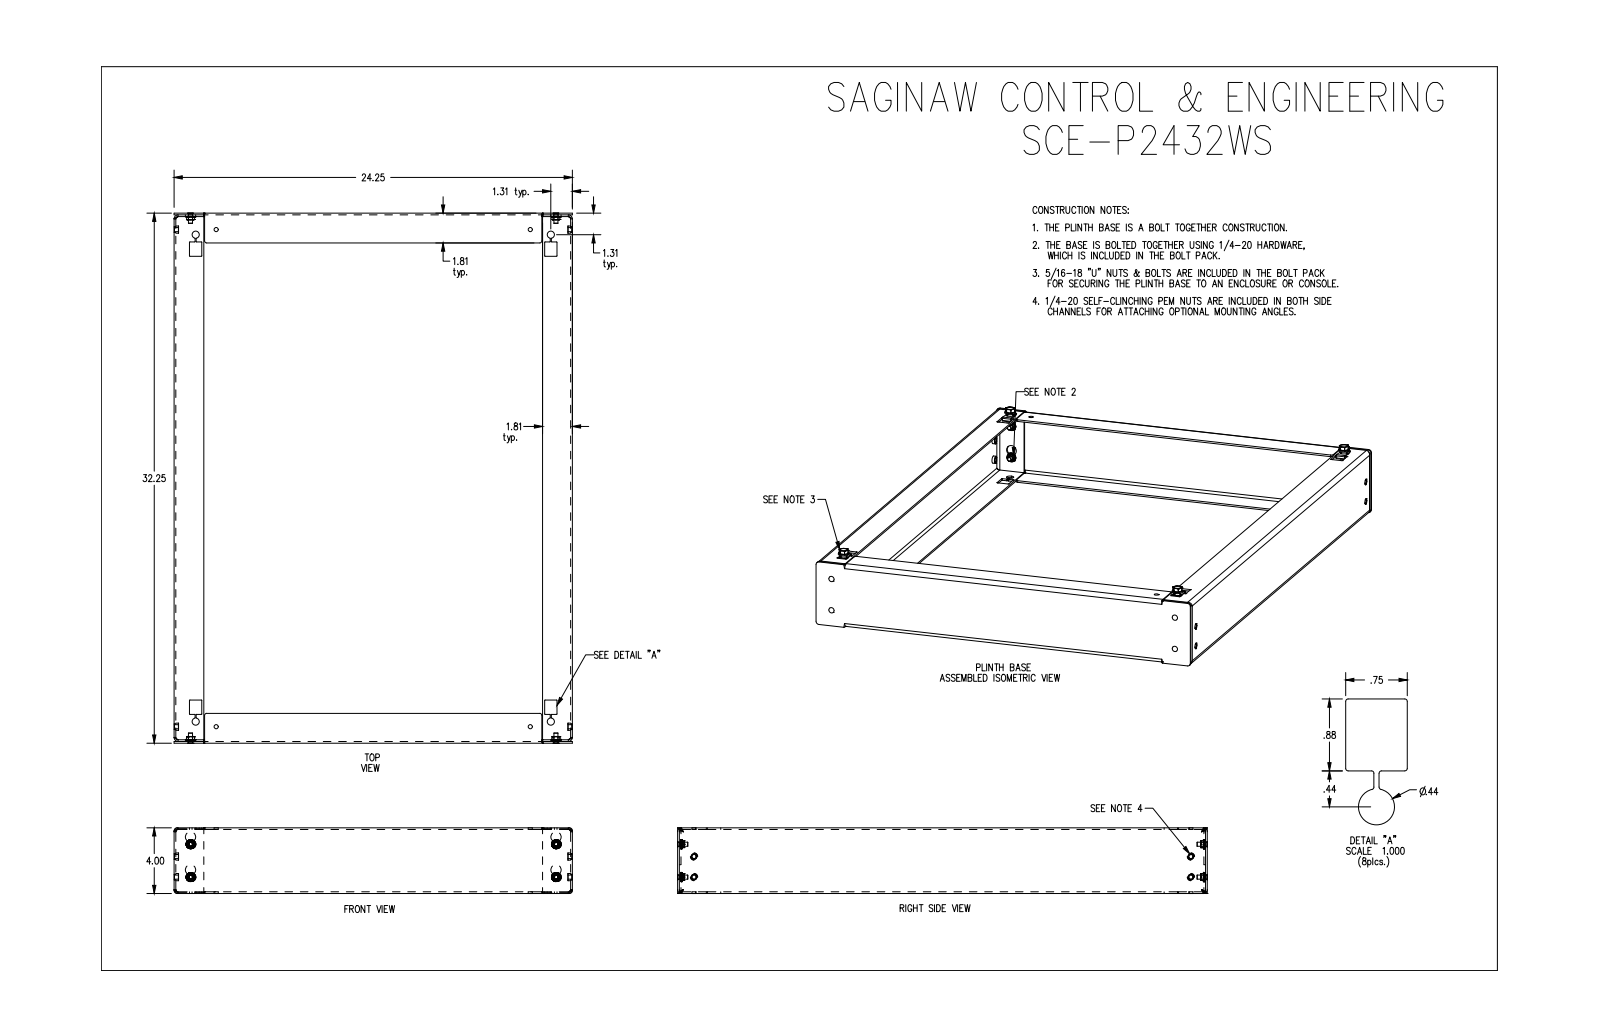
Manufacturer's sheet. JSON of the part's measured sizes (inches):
{"part_name": "SCE-P2432WS", "step_written_by": "SolidWorks 2021 (AUTOMOTIVE_DESIGN)", "units": "inches", "bodies": {"solids": 36, "faces": 2626, "planar": 870, "cylindrical": 364, "other": 1392}, "overall_size": [32.258, 24.25, 4.51], "volume_in3": 85.19, "surface_area_in2": 1685, "round_holes": [[0.25, 12], [0.25, 4], [0.32, 4], [0.344, 4], [0.437, 4], [0.625, 4]], "round_bosses_or_shafts": [[0.563, 4], [0.44, 4], [0.37, 4], [0.343, 4], [0.337, 4], [0.31, 4], [0.248, 4]], "partial_cylinders_radius": [[0.03, 46], [0.01, 24], [0.029, 24], [0.132, 8], [0.236, 8], [0.5, 8], [1, 8], [0.06, 6]], "face_to_face_distances": [0.104, 3.896, 24.146, 32.146, 4, 3.792, 32.042, 24.25, 24.042, 32.25], "hole_center_spacings": [0.44, 2, 29.963, 30.25, 1.25, 1.289, 1.289, 1.56]}
